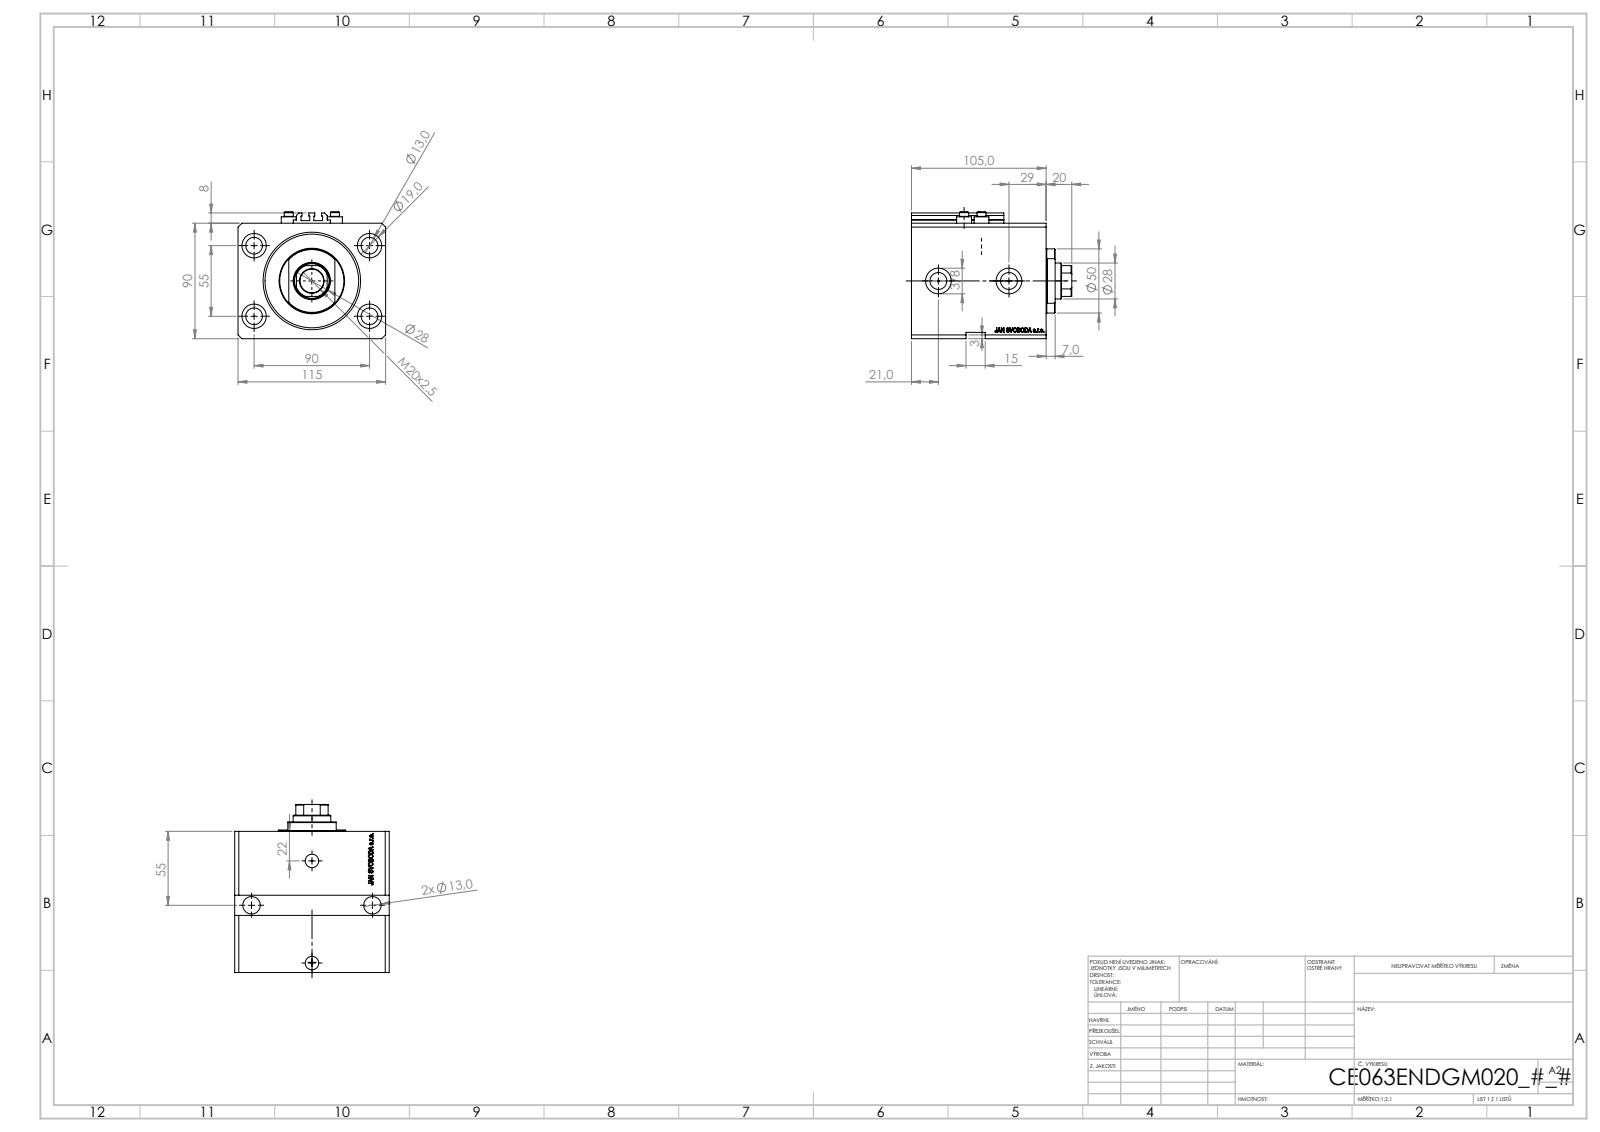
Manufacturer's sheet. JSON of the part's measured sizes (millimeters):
{"part_name": "V250CE_C_VCP; V250CE_E_Body; V250CE_VC_E; ALLEN BOLT V250CE", "step_written_by": "SolidWorks 2019 (CONFIG_CONTROL_DESIGN)", "units": "millimeters", "bodies": {"solids": 8, "faces": 1123, "planar": 547, "cylindrical": 138, "other": 438}, "overall_size": [125, 115, 99], "volume_mm3": 950937, "surface_area_mm2": 155133, "round_holes": [[13, 6], [1.25, 4], [4, 4], [19, 4], [10, 2], [13.16, 2], [20, 2], [18.5, 1], [28, 1], [63, 1], [76, 1]], "round_bosses_or_shafts": [[11.6, 4], [7, 4], [50, 1]], "partial_cylinders_radius": [[0.2, 10], [13.5, 1]], "face_to_face_distances": [90, 20, 115, 85, 105, 87.1, 17.9, 67.1, 40, 65], "hole_center_spacings": [52.74, 55, 90, 13.6, 27.39, 28.46, 33.62, 36]}
